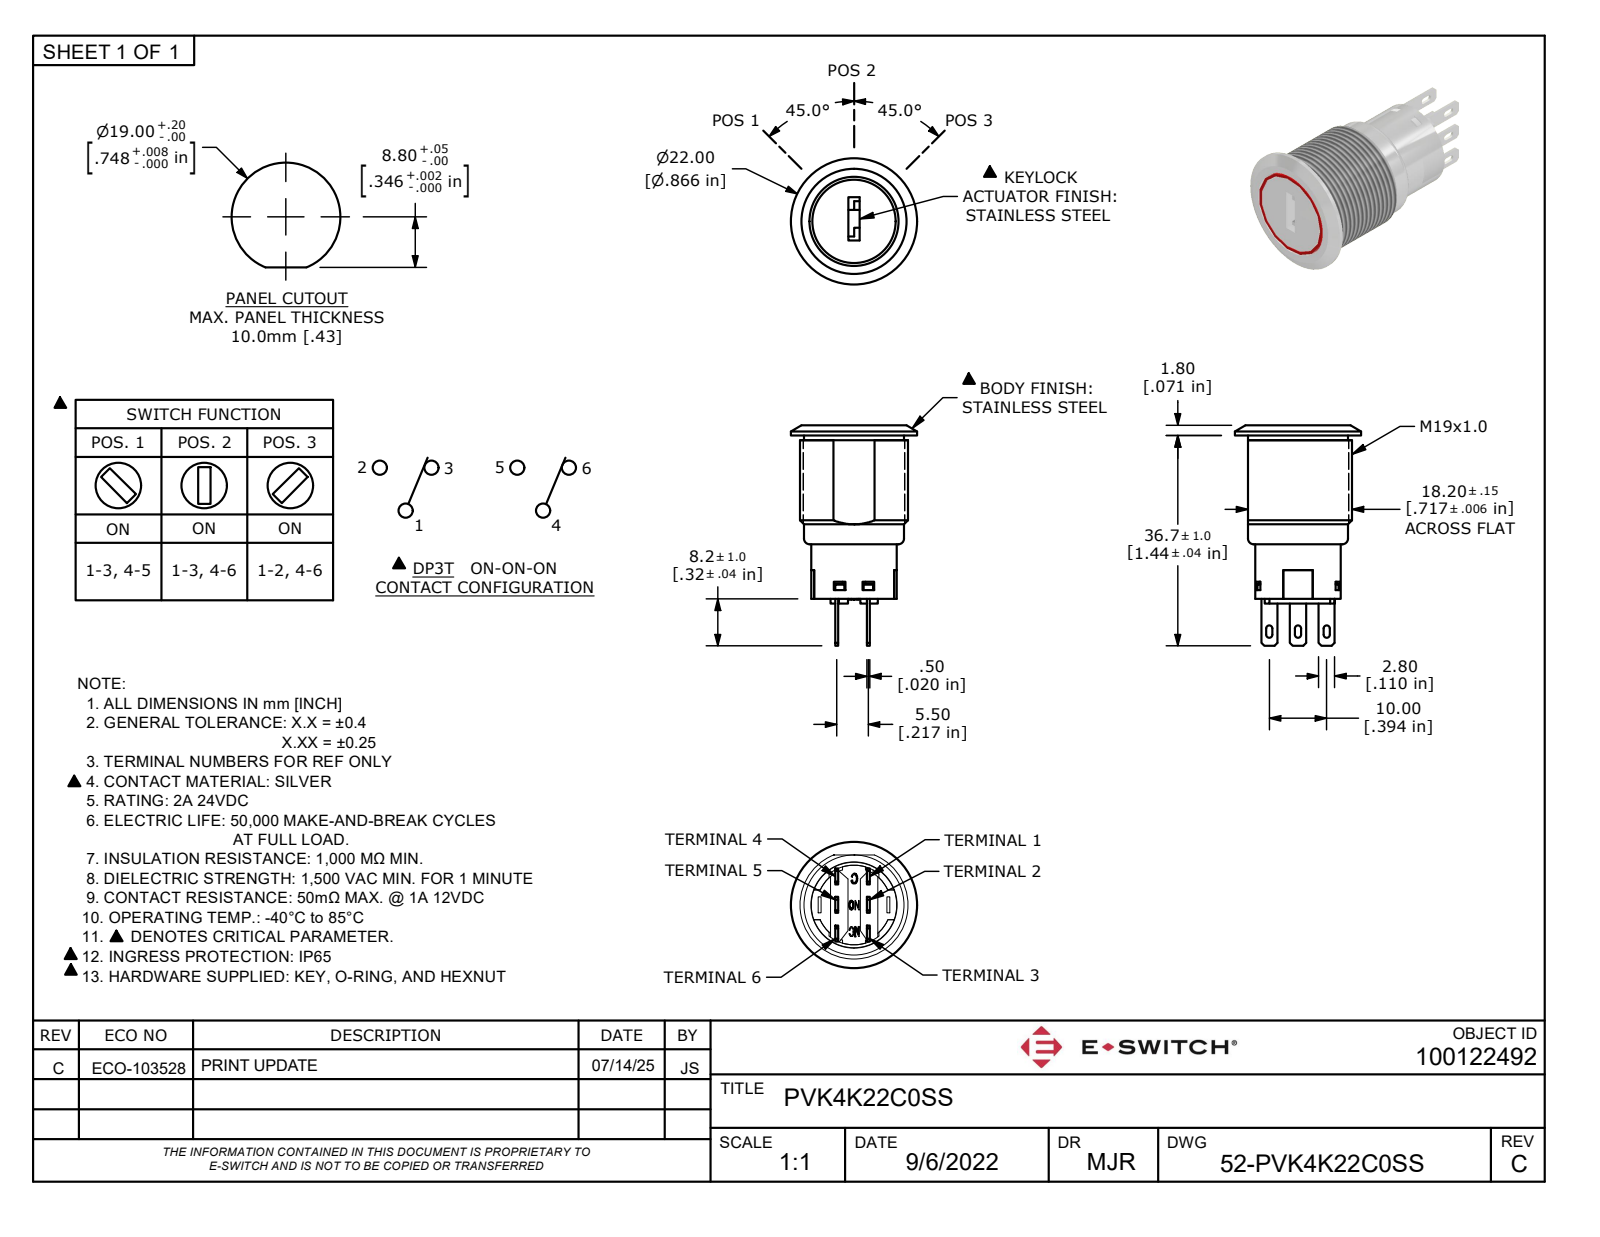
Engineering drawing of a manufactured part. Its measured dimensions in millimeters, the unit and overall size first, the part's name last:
Units: millimetres
Overall size (bounding box): 38.5 × 22 × 22
Round holes (diameter × count): ⌀13.7 ×1, ⌀15 ×1, ⌀17.5 ×1, ⌀22 ×1
Round bosses / shafts (diameter × count): ⌀18.9 ×1, ⌀15.8 ×1, ⌀15.5 ×1, ⌀14.9 ×1, ⌀14.5 ×1
Partial cylindrical surfaces — rounded edges, fillets, slot ends (radius × count): R0.55 ×6, R6.45 ×1, R6.95 ×1
Main face-to-face distances: 0.4, 1.4, 1.8, 15.3, 16.7, 0.5, 5.5, 13.2, 5, 30.3
Volume: 9 414 mm³ · Surface area: 4 027 mm²
Bodies: 2 solids, 259 faces (184 planar, 39 cylindrical, 36 other)
Part name (STEP PRODUCT): PVK4K22C0SS
STEP written by: Autodesk Inventor 2022 (AUTOMOTIVE_DESIGN)
